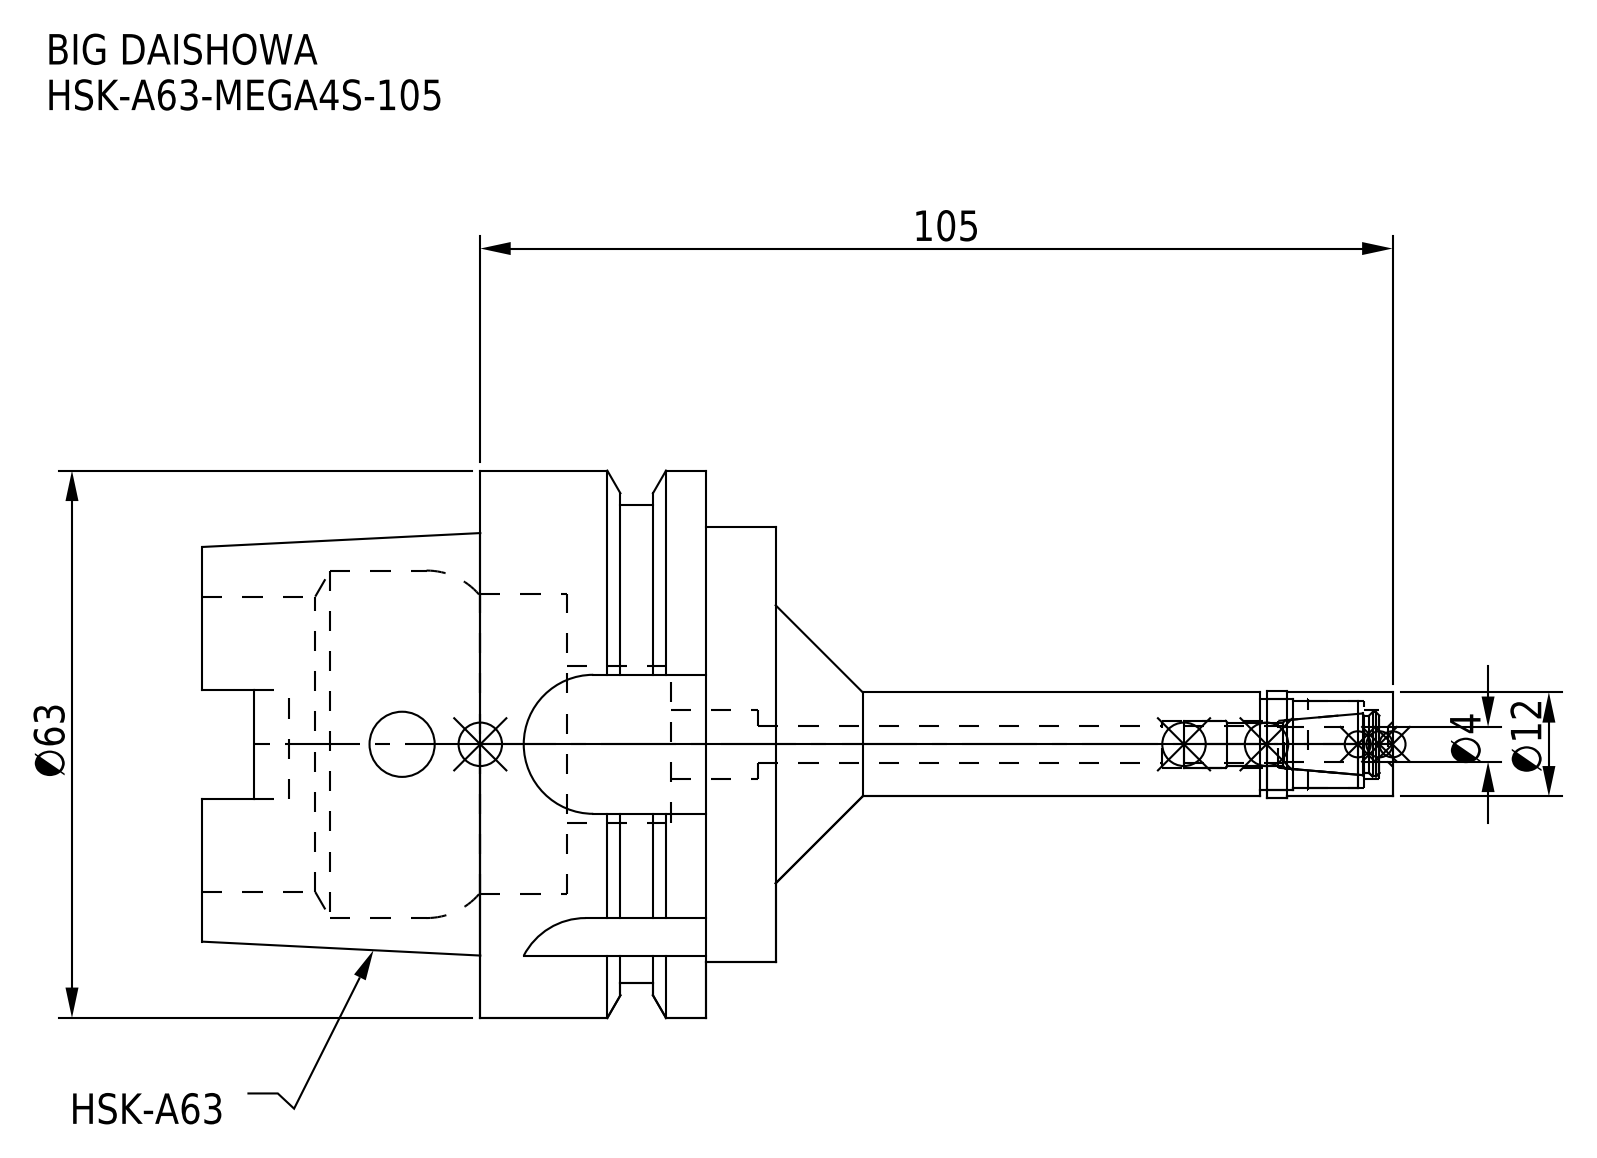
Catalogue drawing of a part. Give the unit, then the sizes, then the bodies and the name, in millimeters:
Units: millimetres
Overall size (bounding box): 137 × 63 × 63
Round holes (diameter × count): ⌀4.1 ×1, ⌀4.2 ×1, ⌀5.4 ×1, ⌀7.5 ×1, ⌀8 ×1, ⌀10 ×1, ⌀10.5 ×1, ⌀18 ×1, ⌀34 ×1, ⌀34.5 ×1, ⌀40 ×1
Round bosses / shafts (diameter × count): ⌀63 ×1, ⌀55 ×1, ⌀50 ×1, ⌀12.3 ×1, ⌀12 ×1
Partial cylindrical surfaces — rounded edges, fillets, slot ends (radius × count): R2.88 ×4, R8 ×4
Main face-to-face distances: 34, 26, 8, 24.05, 16.05, 9.95, 32, 58, 66, 41.95
Volume: 106 560 mm³ · Surface area: 28 336 mm²
Bodies: 2 solids, 122 faces (47 planar, 55 cylindrical, 20 other)
Part name (STEP PRODUCT): HA63MS040105-040_ASM.stp; HSK-A63-MEGA4S-105-040.stp; MGN4S_1.stp; HSK-A63-MEGA4S-105_1.stp (+3 more)
STEP written by: SolidWorks 2019 (CONFIG_CONTROL_DESIGN)
